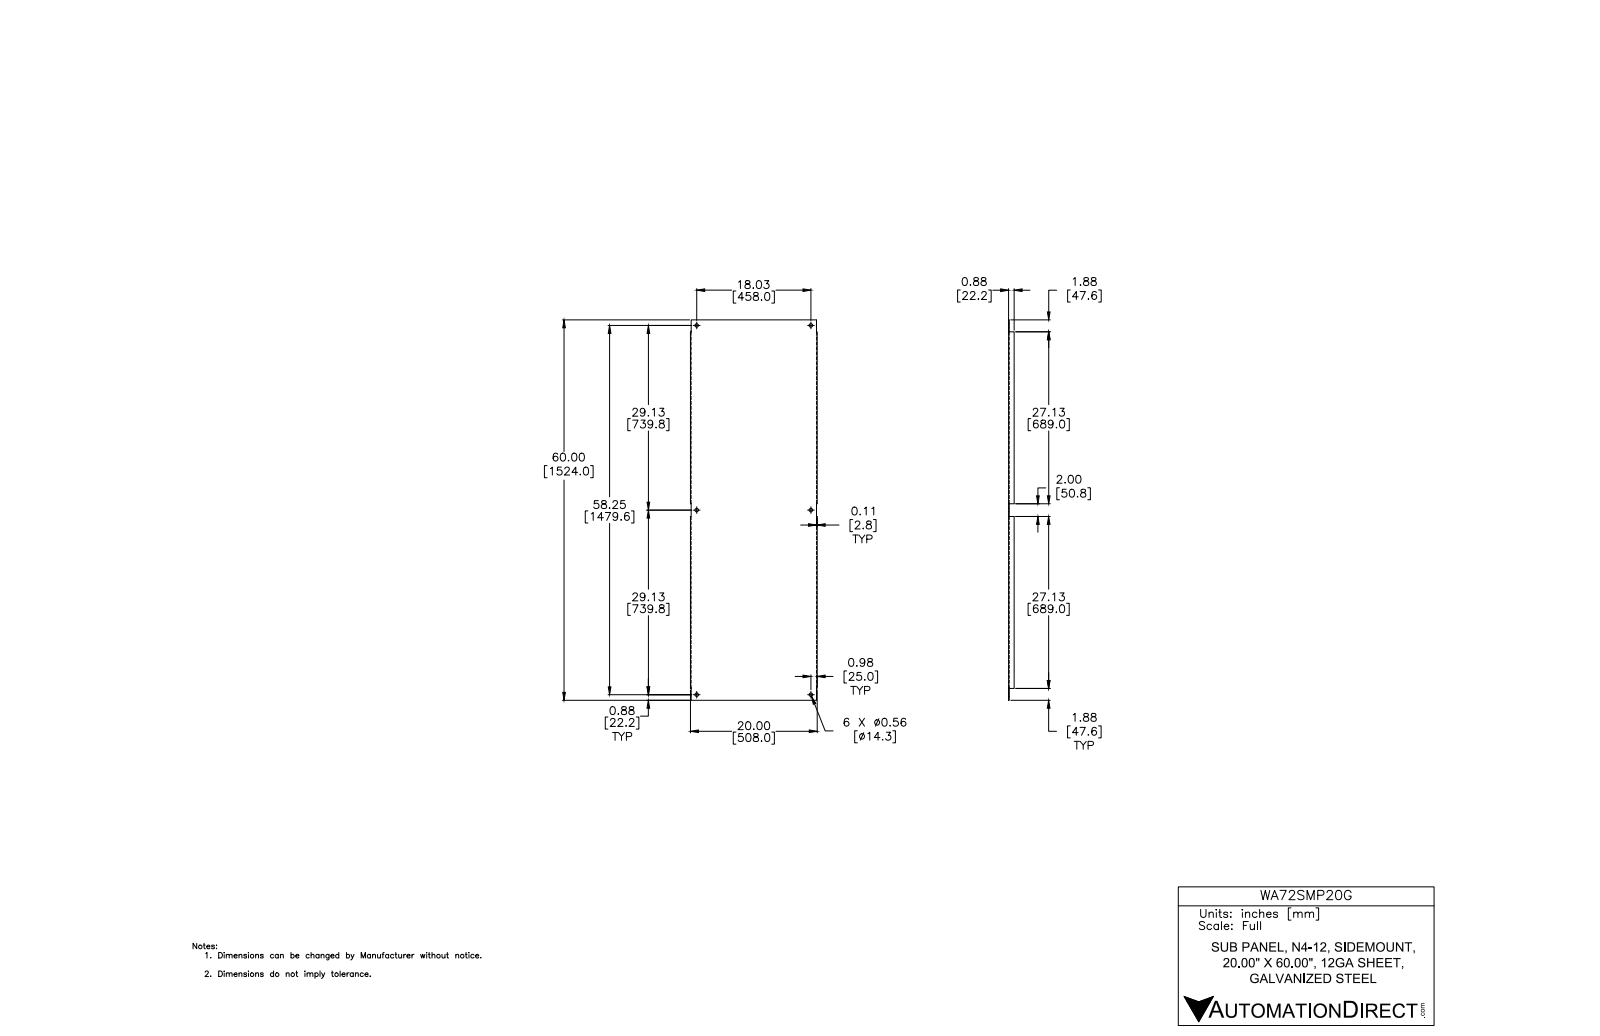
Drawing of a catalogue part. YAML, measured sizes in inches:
part_name: "WA60SMP14G-WA90SMP20G"
step_written_by: "Autodesk Inventor 2012 (AUTOMOTIVE_DESIGN)"
units: inches
bodies: {solids: 1, faces: 48, planar: 34, cylindrical: 14, other: 0}
overall_size: [60, 20, 0.875]
volume: 119.9
surface_area: 2575
round_holes:
  - {diameter: 0.563, count: 6}
partial_cylinders:
  - {radius: 0.015, count: 2}
  - {radius: 0.109, count: 2}
face_to_face_distances: [0.094, 19.906, 19.813, 20, 0.781, 0.875, 60, 0.109, 19.891, 0.015]
hole_center_spacings: [29.125, 34.256, 18.032, 58.25, 60.978]
